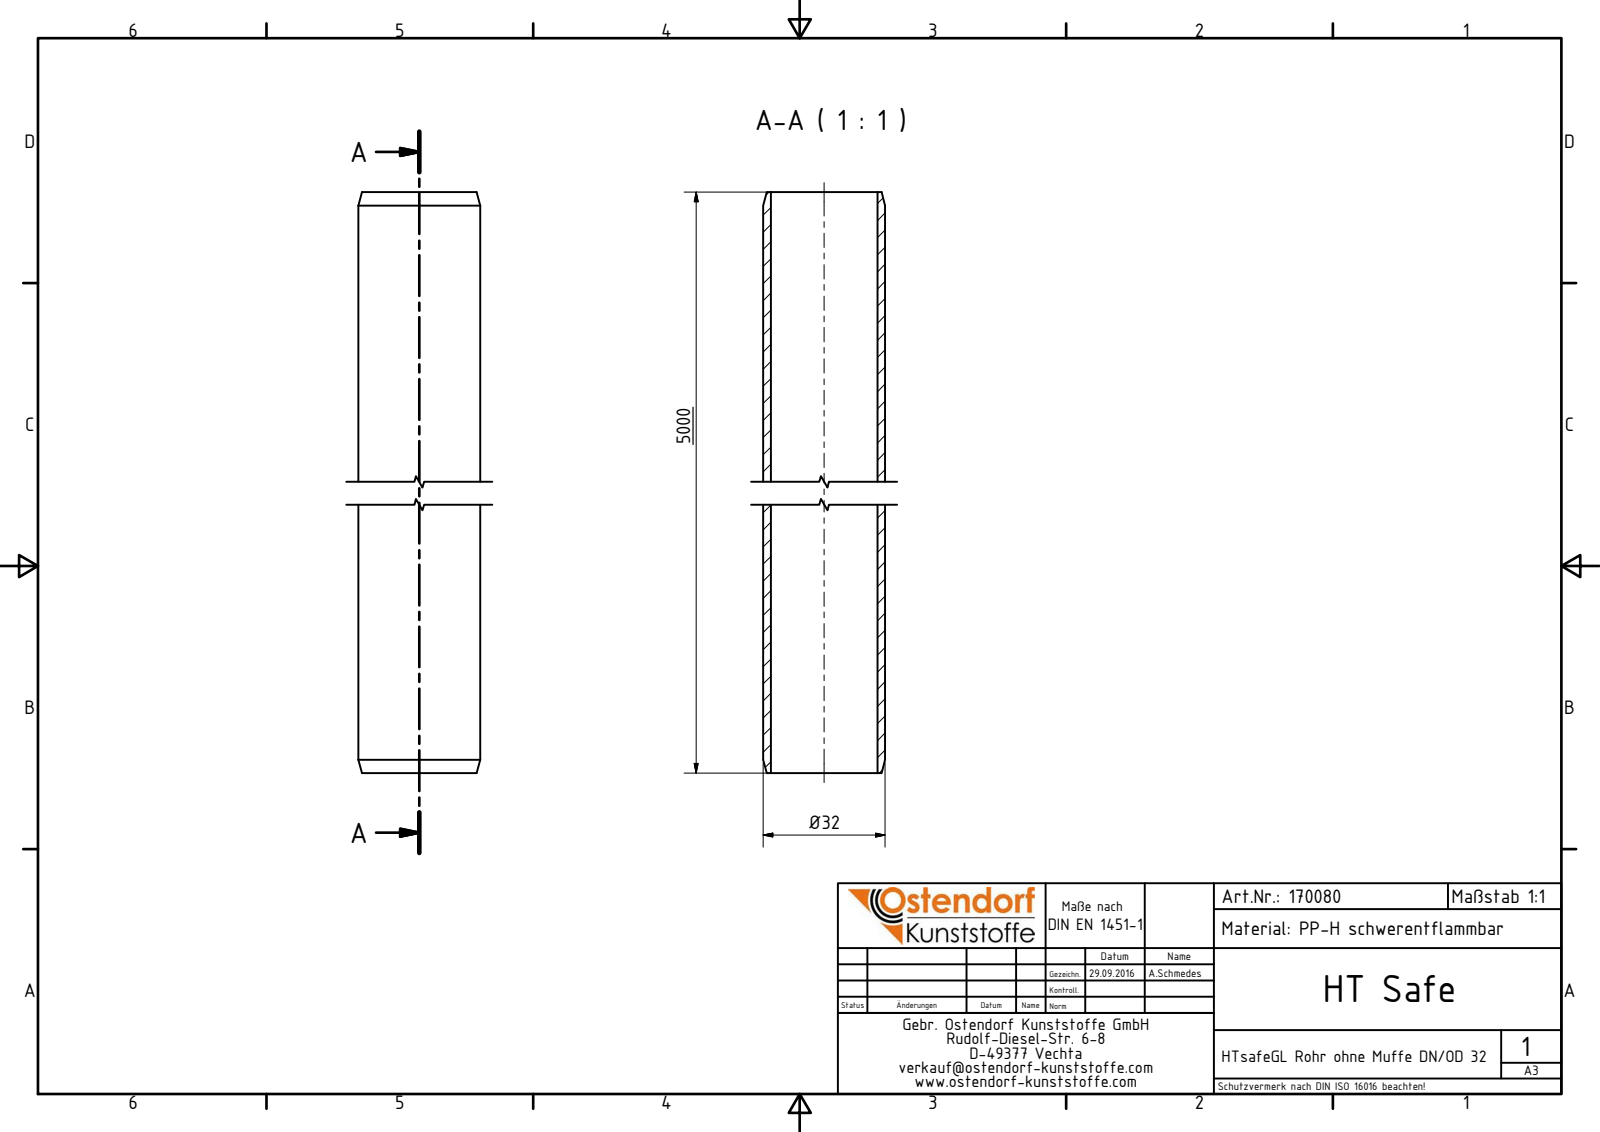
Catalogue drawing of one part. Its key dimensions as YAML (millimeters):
part_name: "170080 HTsafeGL DN_OD 32x5000"
step_written_by: "Autodesk Inventor 2016 (AUTOMOTIVE_DESIGN)"
units: millimeters
bodies: {solids: 1, faces: 6, planar: 2, cylindrical: 2, other: 2}
overall_size: [5000, 32, 32]
volume: 942154
surface_area: 942675
round_holes:
  - {diameter: 28, count: 1}
round_bosses_or_shafts:
  - {diameter: 32, count: 1}
face_to_face_distances: [5000]
